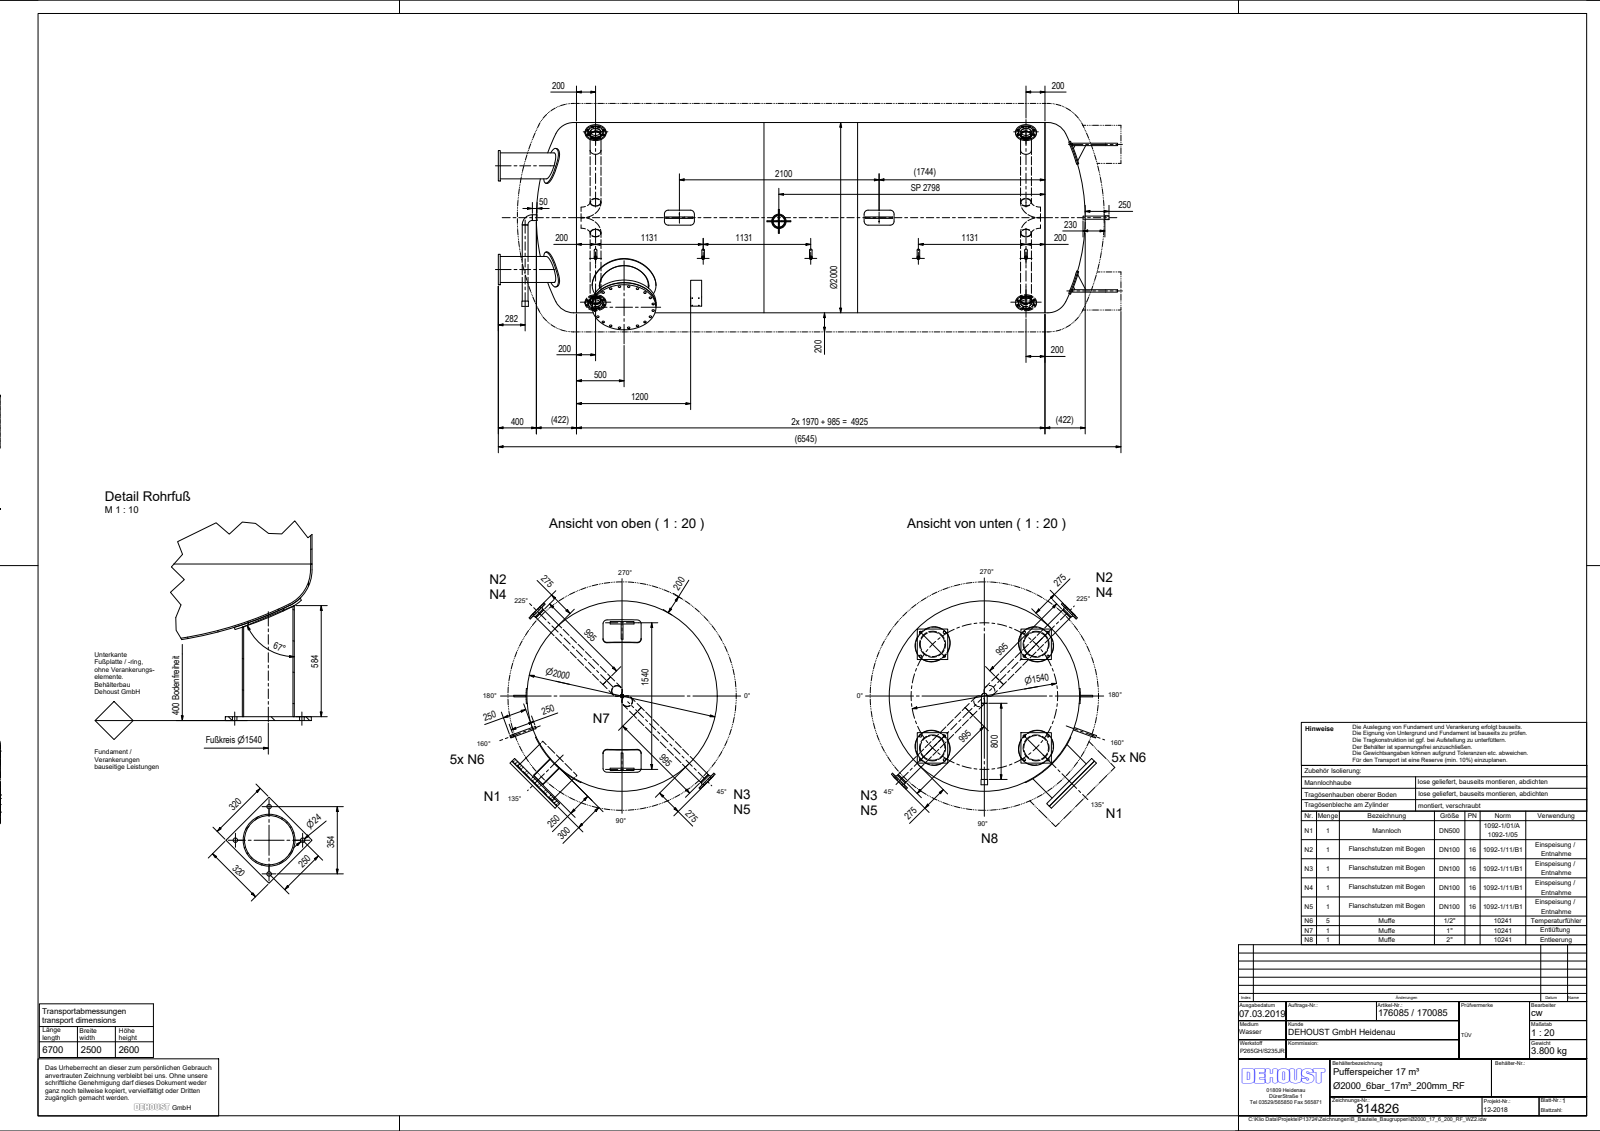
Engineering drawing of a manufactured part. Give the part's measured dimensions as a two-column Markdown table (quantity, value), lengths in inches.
| quantity | value |
| --- | --- |
| part name | Ø2000_17_6_200_RF_WZ2; Klöpper_Gew_Ø2000_7,8; Zyl_Ø2000_7x4925_mV_2019; TÖB_Puffer_Ø2000_7, 8_200 (+8 more) |
| STEP written by | Autodesk Inventor 2019 (AUTOMOTIVE_DESIGN) |
| units | inches |
| bodies | 59 solids, 457 faces (178 planar, 229 cylindrical, 50 other) |
| overall size | 256.318 × 85.793 × 85.75 |
| volume | 26 550 in³ |
| surface area | 144 600 in² |
| round holes (diameter × count) | 1.024 × 40, 0.709 × 32, 0.945 × 16, 0.733 × 5, 0.854 × 5, 1.059 × 5, 0.228 × 4, 4.185 × 4, 4.217 × 4, 4.5 × 4, 10.189 × 4, 0.197 × 2 |
| round bosses / shafts (diameter × count) | 1.059 × 5, 1.039 × 5, 14.961 × 4, 10.748 × 4, 8.661 × 4, 6.22 × 4, 4.5 × 4, 26.378 × 3 |
| partial cylindrical surfaces (radius × count) | 1.654 × 16, 0.394 × 6, 0.236 × 4, 0.197 × 2, 1.417 × 2, 2.835 × 2, 4.921 × 1, 39.646 × 1 |
| main face-to-face distances | 0.787, 15.748, 1.102, 21.949, 37.697, 38.681, 0.984, 22.933, 60.63, 85.925 |
| hole center spacings | 3.543, 12.205, 178.15, 44.537, 7.543, 5.011, 6.547, 21.749 |
